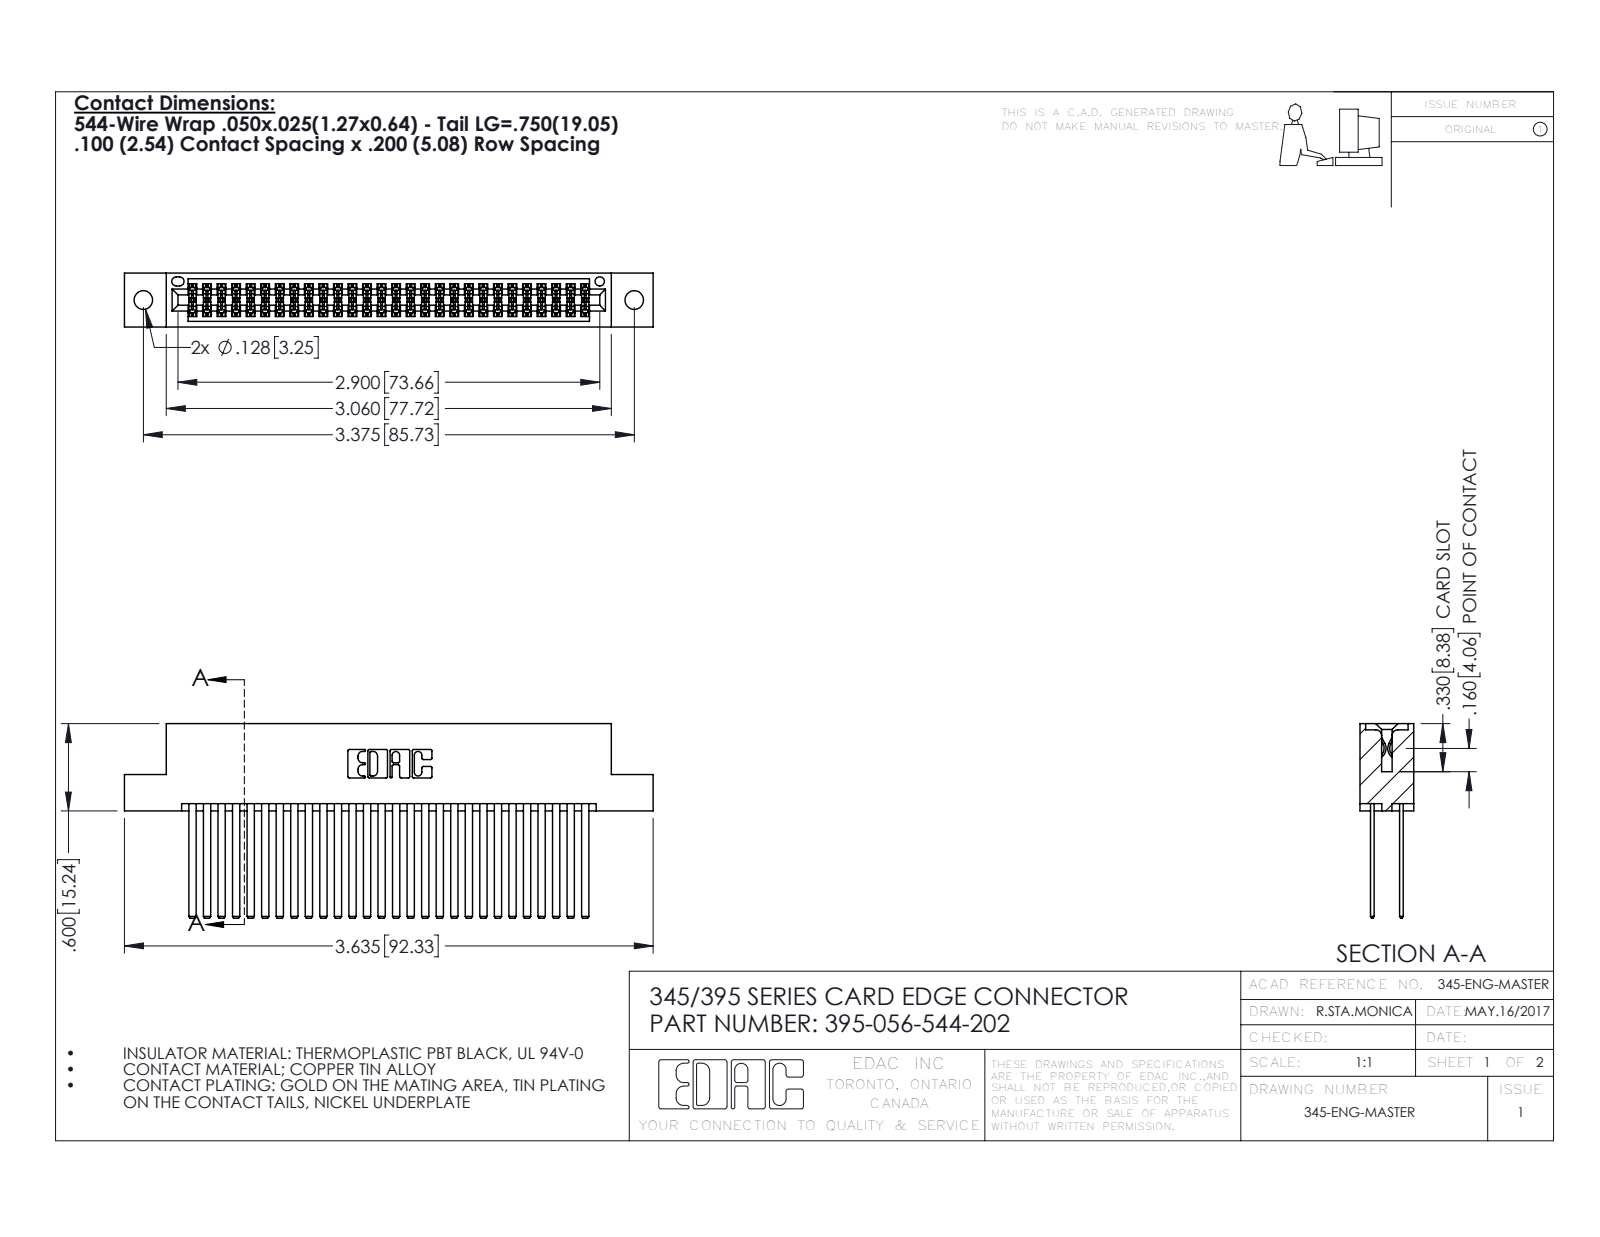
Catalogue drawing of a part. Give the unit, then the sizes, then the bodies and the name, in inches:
Units: inches
Overall size (bounding box): 3.635 × 1.337 × 0.37
Round holes (diameter × count): ⌀0.128 ×2, ⌀0.064 ×1
Partial cylindrical surfaces — rounded edges, fillets, slot ends (radius × count): R0.006 ×84, R0.01 ×22, R0.007 ×6, R0.031 ×6, R0.026 ×3, R0.014 ×2, R0.019 ×2, R0.022 ×2
Main face-to-face distances: 0.2, 0.025, 0.298, 0.072, 0.272, 0.098, 0.225, 0.175, 0.37, 0.05
Hole centre spacings: 0.27, 3.14, 3.375
Volume: 0.585 in³ · Surface area: 24.69 in²
Bodies: 57 solids, 2590 faces (1704 planar, 886 cylindrical, 0 other)
Part name (STEP PRODUCT): 395-056-544-202; 345-292-001_345-293-144; 345 Part_Flush Mounting Lugs - 0.128 Dia
STEP written by: SolidWorks 2016 (CONFIG_CONTROL_DESIGN)
